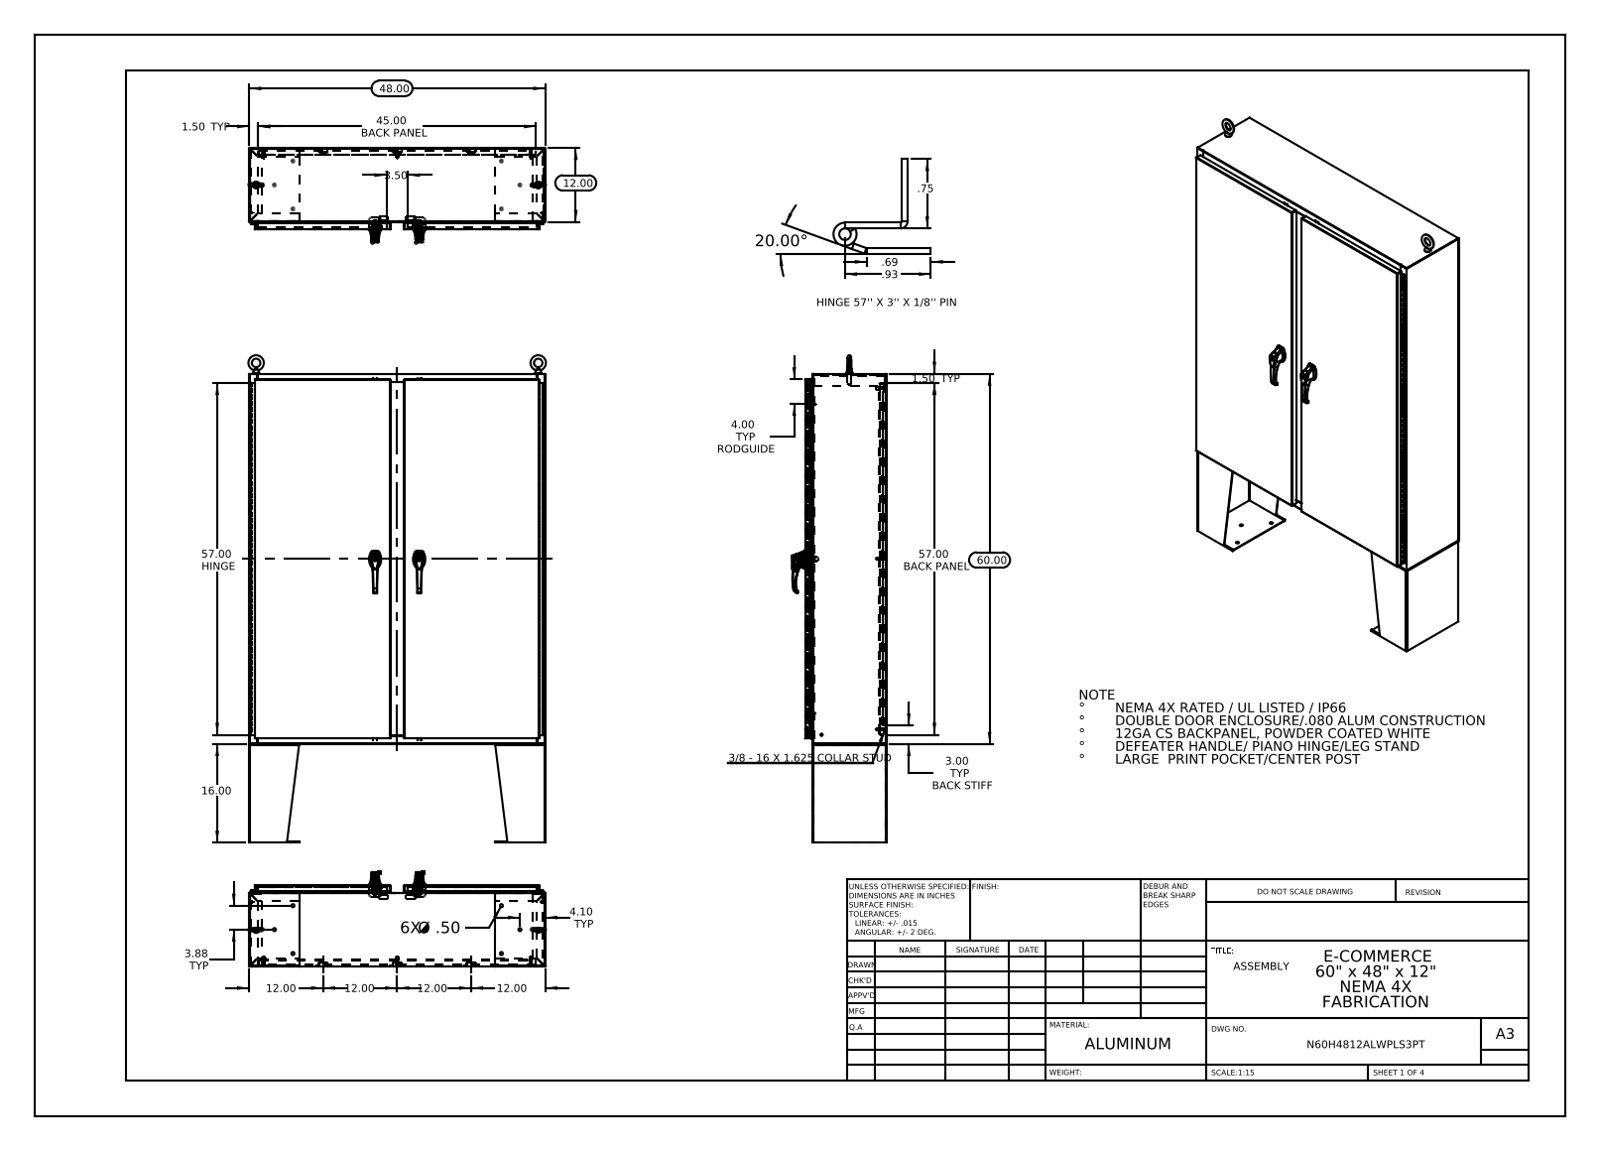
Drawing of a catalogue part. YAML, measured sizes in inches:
part_name: "Quarter-20 CD Stud; 022151; 21130102; N60H4812SSWPLS3PT Hinge Enclosure Side DoubleDoor (+8 more)"
step_written_by: "SolidWorks 2013 (CONFIG_CONTROL_DESIGN)"
units: inches
bodies: {solids: 66, faces: 6660, planar: 2654, cylindrical: 2642, other: 1364}
overall_size: [79, 48.226, 15.307]
volume: 1179
surface_area: 28453
round_holes:
  - {diameter: 0.5, count: 14}
  - {diameter: 0.25, count: 8}
  - {diameter: 0.138, count: 6}
  - {diameter: 0.161, count: 6}
  - {diameter: 0.079, count: 4}
  - {diameter: 0.313, count: 4}
  - {diameter: 0.437, count: 4}
  - {diameter: 0.75, count: 4}
  - {diameter: 0.125, count: 2}
  - {diameter: 0.125, count: 2}
  - {diameter: 0.197, count: 2}
  - {diameter: 0.203, count: 2}
round_bosses_or_shafts:
  - {diameter: 0.625, count: 10}
  - {diameter: 0.375, count: 8}
  - {diameter: 0.33, count: 8}
  - {diameter: 0.315, count: 5}
  - {diameter: 0.236, count: 5}
  - {diameter: 1.181, count: 2}
  - {diameter: 0.748, count: 2}
  - {diameter: 0.68, count: 2}
partial_cylinders:
  - {radius: 0.118, count: 72}
  - {radius: 0.006, count: 66}
  - {radius: 0.013, count: 44}
  - {radius: 0.088, count: 36}
  - {radius: 0.039, count: 28}
  - {radius: 0.028, count: 24}
  - {radius: 0.008, count: 12}
  - {radius: 0.02, count: 12}
face_to_face_distances: [0.075, 13.126, 0.104, 1.075, 13.051, 1, 12.051, 1.179, 1.104, 11.947]
hole_center_spacings: [7.152, 7.156, 7.157, 23.366, 25.674, 0.295, 0.625, 0.841]
